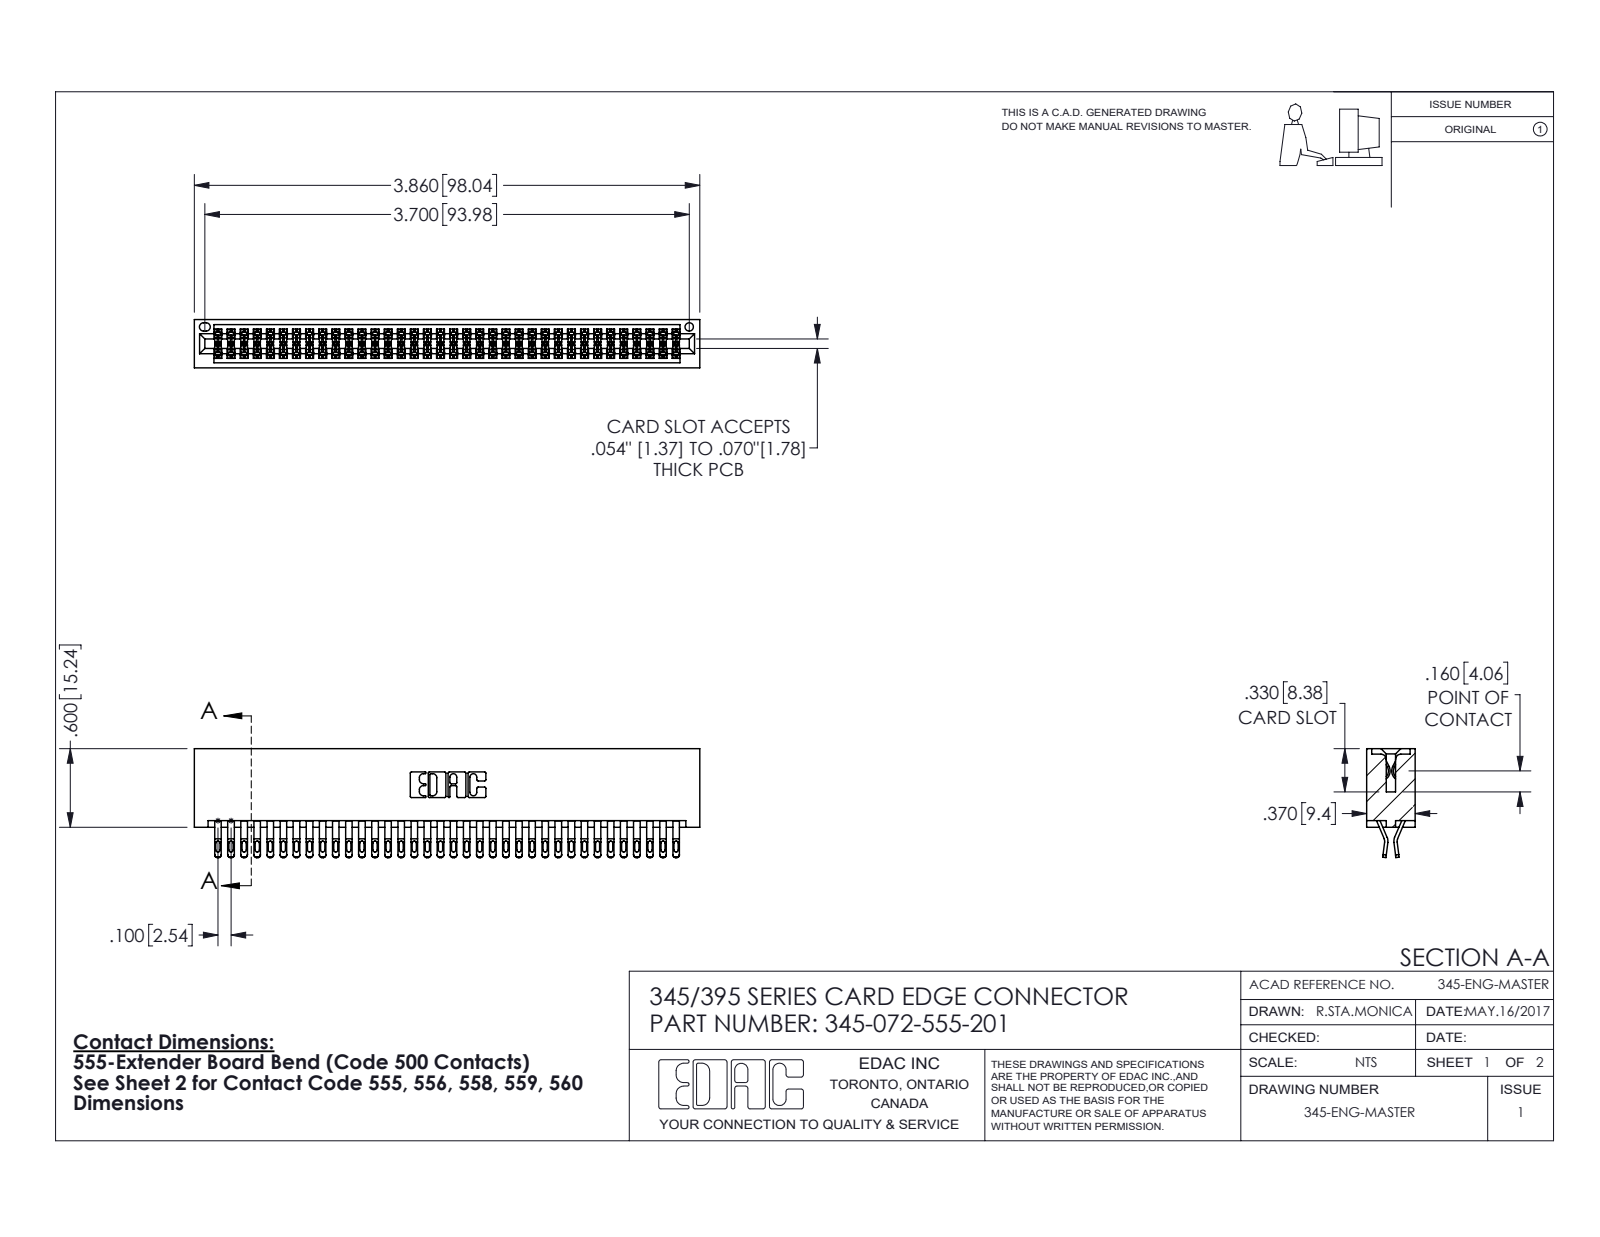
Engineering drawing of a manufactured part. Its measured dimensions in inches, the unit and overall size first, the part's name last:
Units: inches
Overall size (bounding box): 3.86 × 0.832 × 0.37
Round holes (diameter × count): ⌀0.064 ×1
Partial cylindrical surfaces — rounded edges, fillets, slot ends (radius × count): R0.016 ×180, R0.02 ×144, R0.006 ×108, R0.01 ×22, R0.007 ×6, R0.031 ×6, R0.026 ×3, R0.01 ×2
Main face-to-face distances: 0.298, 0.072, 0.025, 0.2, 0.37, 0.098, 0.272, 0.225, 0.175, 0.149
Volume: 0.628 in³ · Surface area: 25 in²
Bodies: 73 solids, 4150 faces (2308 planar, 1842 cylindrical, 0 other)
Part name (STEP PRODUCT): 345 Part_No Mounting Lugs; 345-292-001_555 Tail; 345-072-555-201
STEP written by: SolidWorks 2016 (CONFIG_CONTROL_DESIGN)
